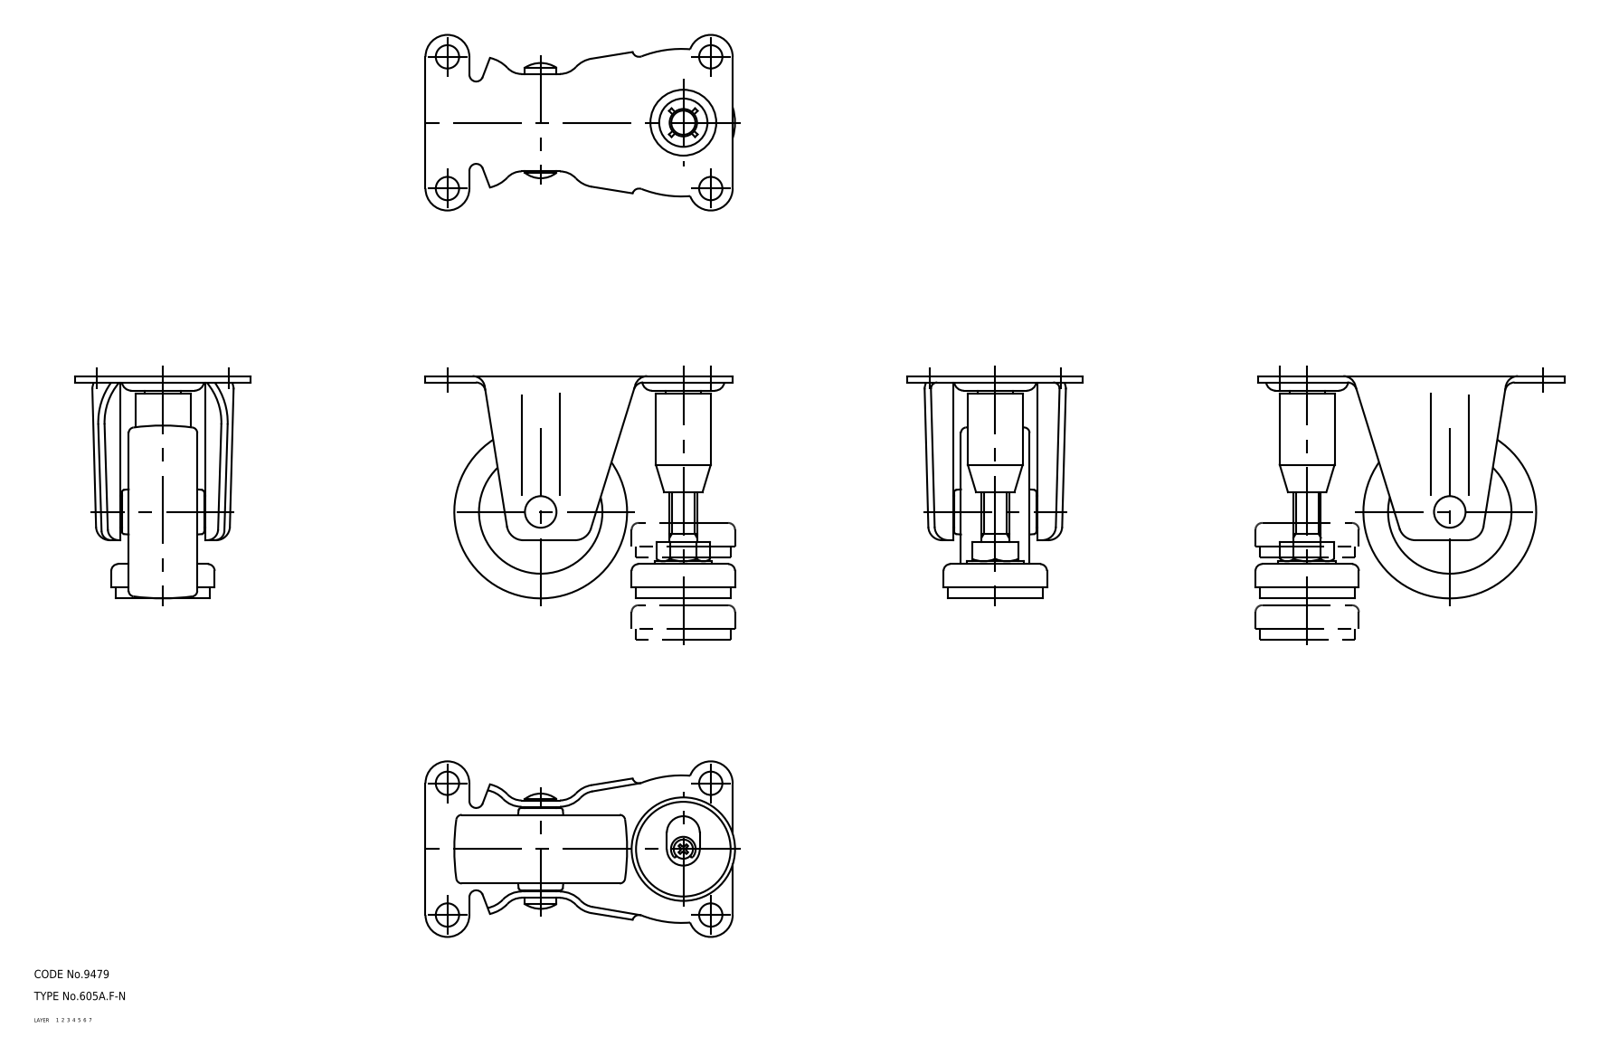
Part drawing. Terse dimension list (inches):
name: 67121998; 67122011; 67122024; 67122037
written by: CADfix (AUTOMOTIVE_DESIGN)
unit: in
bodies: 4 solids, 227 faces (0 planar, 0 cylindrical, 227 other)
size: 4.443 × 3.189 × 2.52
volume: 6.964 in³; area: 70.55 in²
